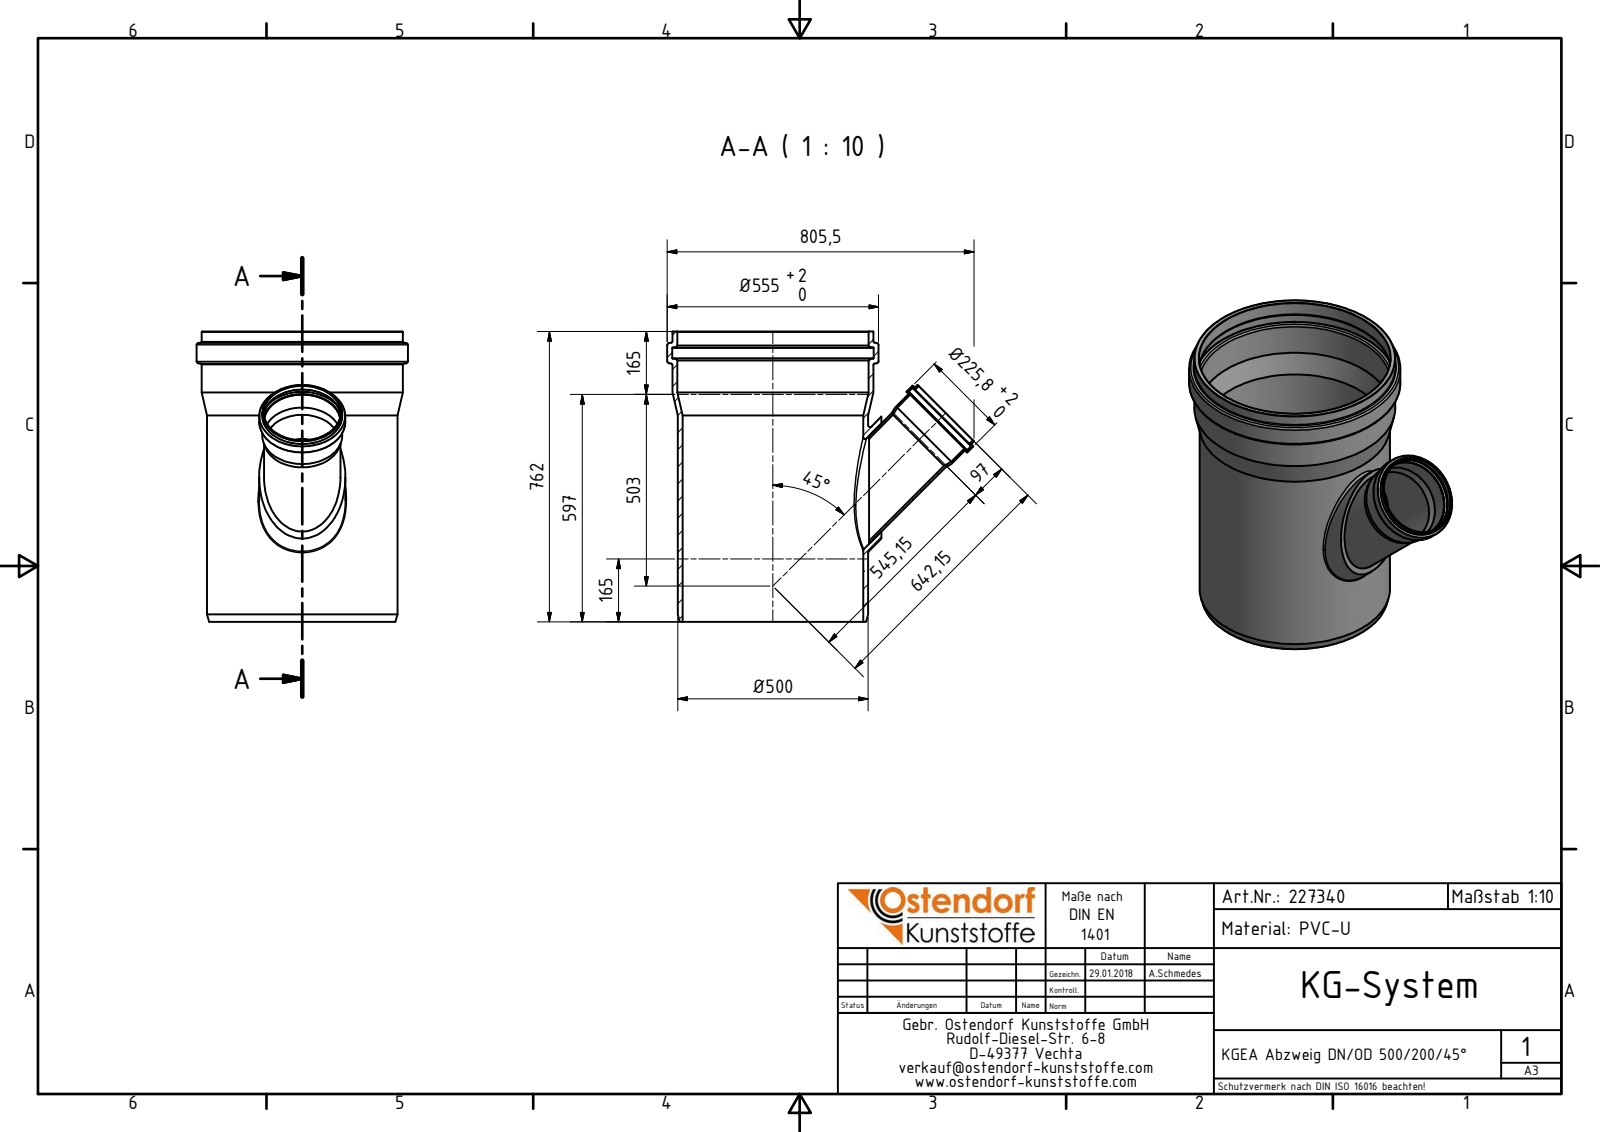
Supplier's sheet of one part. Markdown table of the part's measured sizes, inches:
| quantity | value |
| --- | --- |
| part name | 227340 KGEA Abzweig DN_OD 500_200_45°; 227340 KGEA Abzweig DN_OD 500_200_45° Abzweig |
| STEP written by | Autodesk Inventor 2016 (AUTOMOTIVE_DESIGN) |
| units | inches |
| bodies | 2 solids, 60 faces (6 planar, 19 cylindrical, 35 other) |
| overall size | 31.713 × 30 × 21.85 |
| volume | 1 025 in³ |
| surface area | 4 435 in² |
| round holes (diameter × count) | 7.909 × 2, 7.453 × 1, 7.894 × 1, 7.898 × 1, 8.543 × 1, 18.661 × 1, 19.764 × 1, 20.827 × 1 |
| round bosses / shafts (diameter × count) | 21.85 × 1, 20.787 × 1, 19.685 × 1, 8.917 × 1, 8.89 × 1, 8.256 × 1, 8.244 × 1, 7.894 × 1 |
| main face-to-face distances | 30, 1.271, 1.25 |
